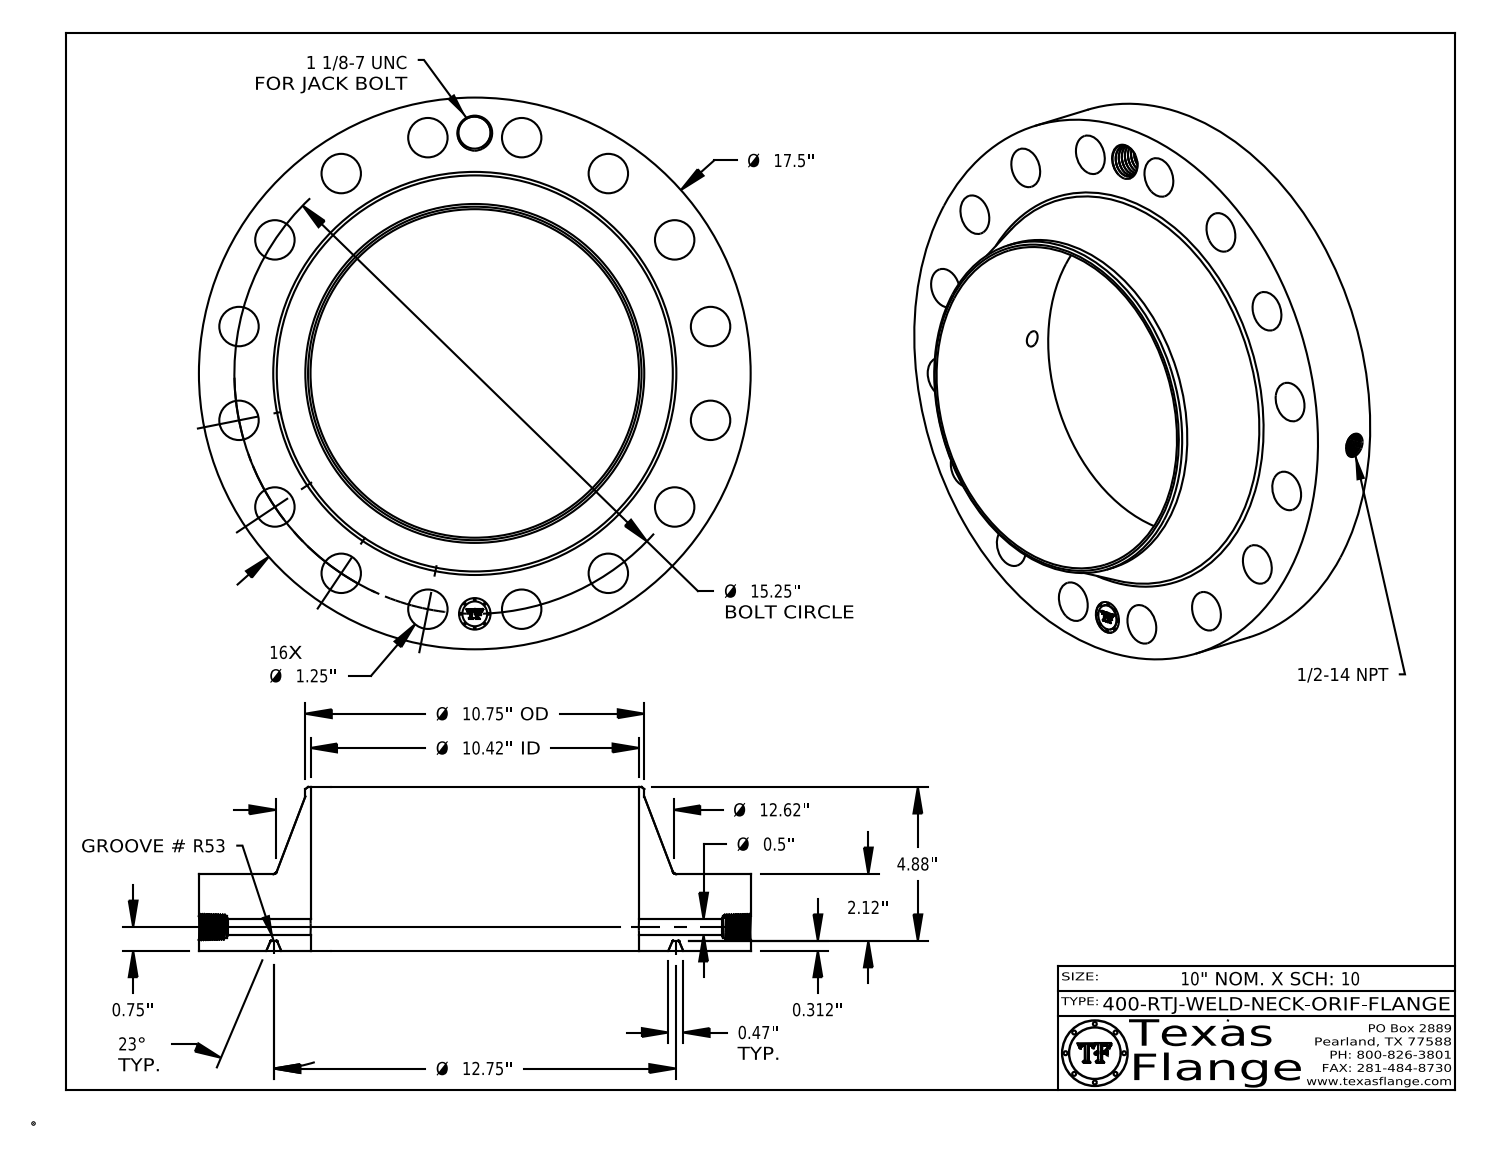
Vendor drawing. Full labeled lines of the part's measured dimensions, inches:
Part name (STEP PRODUCT): 400-RTJ-WELD-NECK
STEP written by: CATIA V5 STEP AP214 (AUTOMOTIVE_DESIGN)
Units: inches
Bodies: 1 solid, 806 faces (370 planar, 112 cylindrical, 324 other)
Overall size (bounding box): 17.5 × 17.5 × 5.192
Volume: 377.8 in³ · Surface area: 838.2 in²
Round holes (diameter × count): ⌀1.25 ×16, ⌀0.5 ×1, ⌀0.672 ×1, ⌀0.984 ×1, ⌀1 ×1, ⌀10.42 ×1
Round bosses / shafts (diameter × count): ⌀0.061 ×8, ⌀17.5 ×1, ⌀10.75 ×1, ⌀0.788 ×1
Main face-to-face distances: 2.432, 0.312, 2.12, 5.192, 4.88, 2.76, 0.015, 2.417, 2.105, 2.775
Hole centre spacings: 5.836, 7.625, 10.783, 14.089, 14.957, 2.975, 2.975, 8.472
